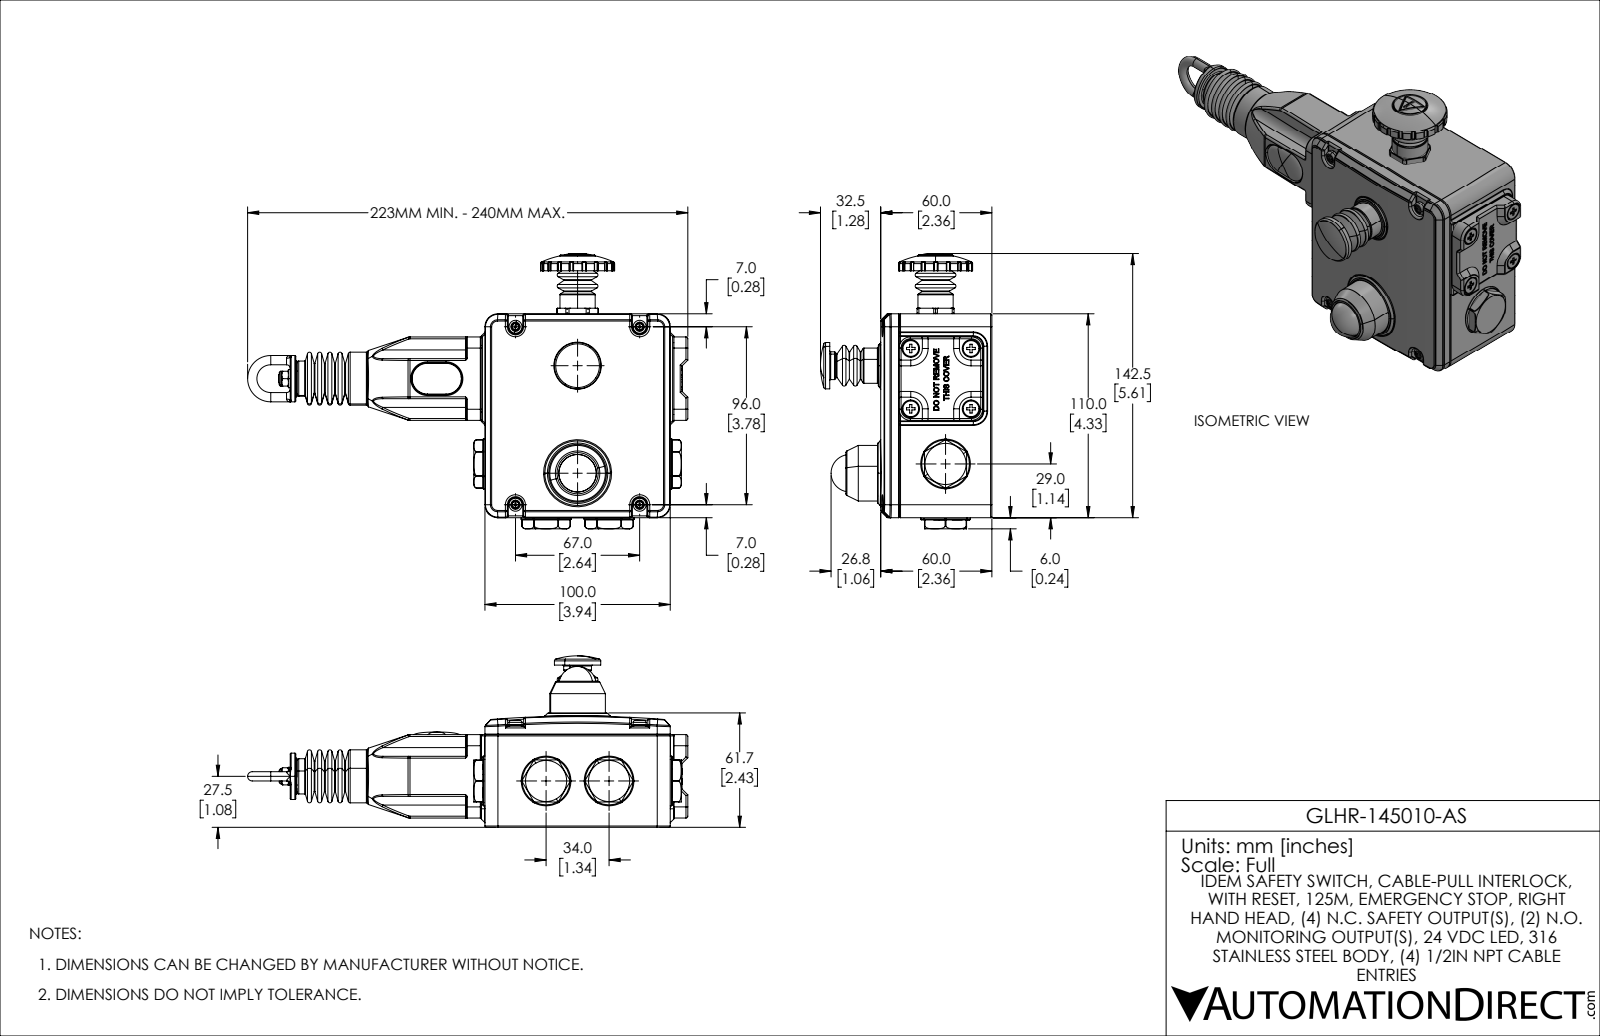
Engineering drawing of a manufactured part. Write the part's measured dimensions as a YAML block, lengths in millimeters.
part_name: "GLHR-SS-145010-AS"
step_written_by: "SolidWorks 2021 (AUTOMOTIVE_DESIGN)"
units: millimeters
bodies: {solids: 47, faces: 4430, planar: 1376, cylindrical: 1434, other: 1620}
overall_size: [238.1, 146.7, 92.8]
volume: 312000
surface_area: 193400
round_holes:
  - {diameter: 5, count: 9}
  - {diameter: 5.3, count: 9}
  - {diameter: 9.6, count: 8}
  - {diameter: 4.1, count: 7}
  - {diameter: 9, count: 6}
  - {diameter: 3.3, count: 4}
  - {diameter: 4, count: 4}
  - {diameter: 4.8, count: 4}
  - {diameter: 5.4, count: 4}
  - {diameter: 5.8, count: 4}
  - {diameter: 1.7, count: 3}
  - {diameter: 2.6, count: 3}
round_bosses_or_shafts:
  - {diameter: 5, count: 11}
  - {diameter: 8.5, count: 8}
  - {diameter: 4.4, count: 8}
  - {diameter: 7, count: 5}
  - {diameter: 20, count: 4}
  - {diameter: 3.5, count: 4}
  - {diameter: 1.3, count: 4}
  - {diameter: 24, count: 3}
partial_cylinders:
  - {radius: 0.5, count: 221}
  - {radius: 1, count: 164}
  - {radius: 0.2, count: 76}
  - {radius: 0.7, count: 48}
  - {radius: 0.3, count: 18}
  - {radius: 0.2, count: 14}
  - {radius: 2, count: 14}
  - {radius: 0.1, count: 10}
face_to_face_distances: [1, 2, 3.5, 55.4, 2.9, 52.5, 102, 4, 110, 8.5]
hole_center_spacings: [32.5, 32.5, 23, 9.5, 5.8, 22.9, 23, 23]
